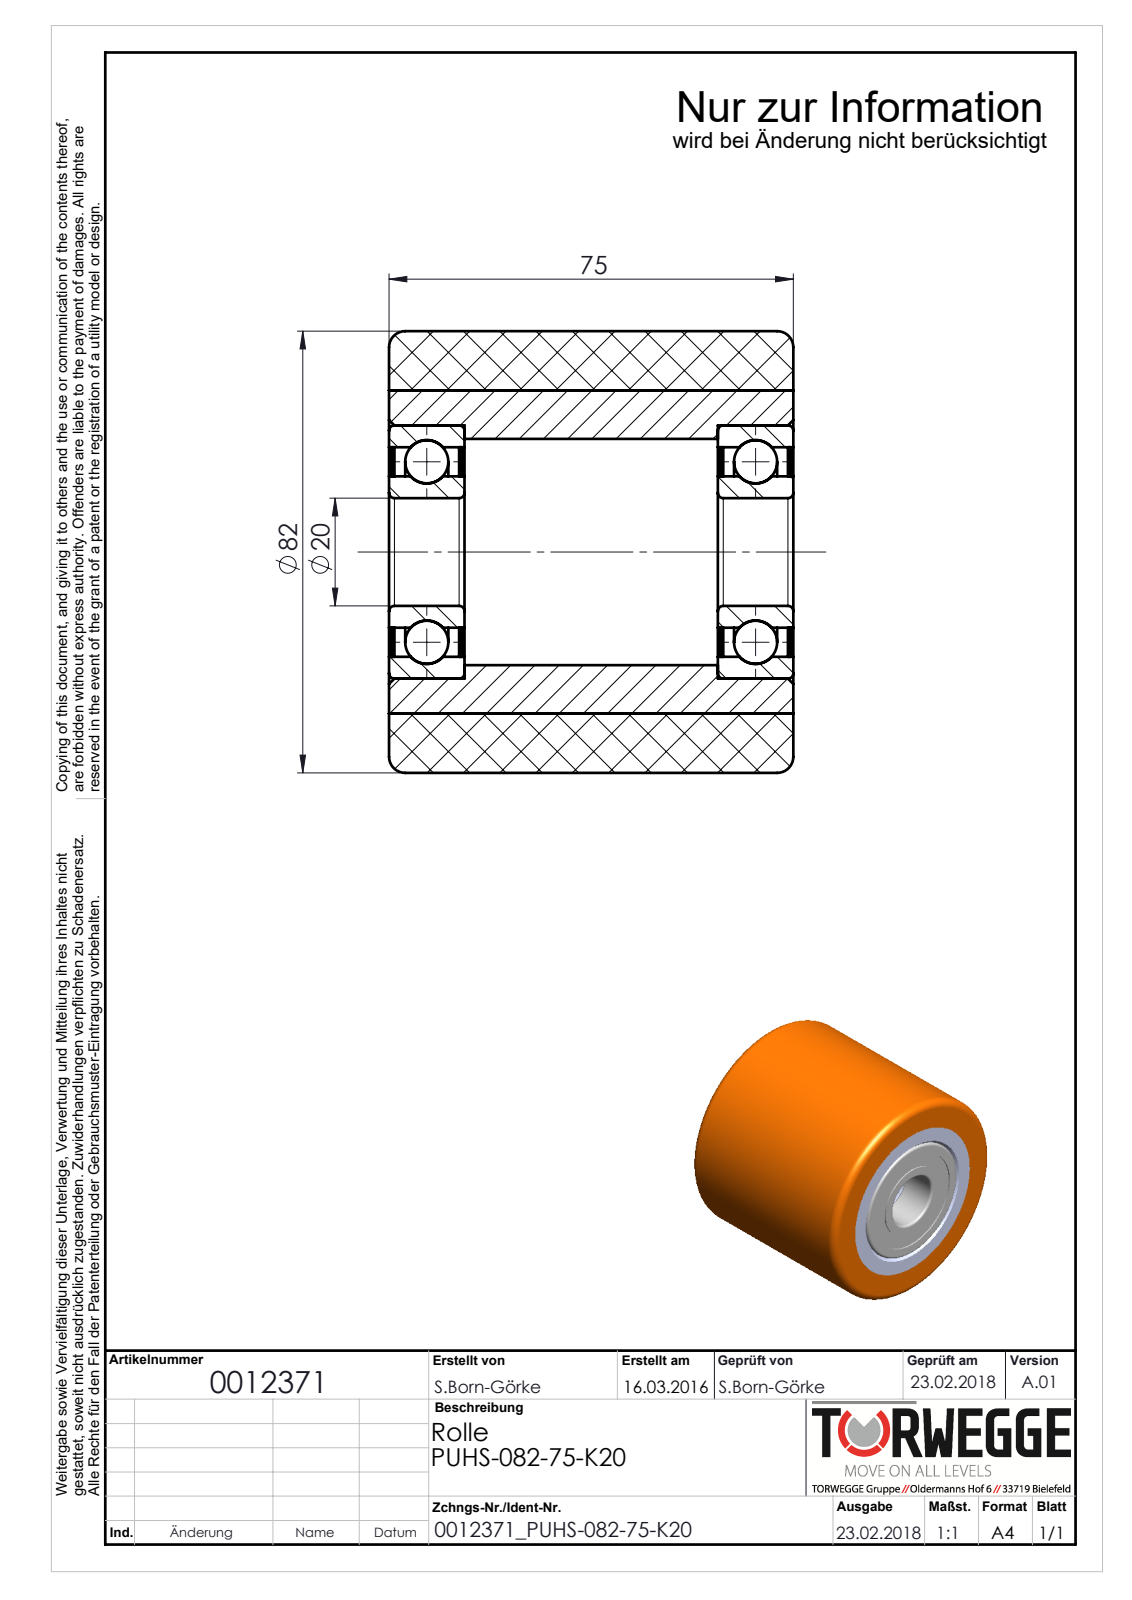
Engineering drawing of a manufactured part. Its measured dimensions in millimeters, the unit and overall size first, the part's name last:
Units: millimetres
Overall size (bounding box): 82 × 82 × 75
Round holes (diameter × count): ⌀20 ×1, ⌀28.1 ×1, ⌀38.9 ×1, ⌀42 ×1, ⌀47 ×1, ⌀60 ×1
Round bosses / shafts (diameter × count): ⌀82 ×1
Main face-to-face distances: 0.5, 61, 13, 75, 1, 13.5, 61.5, 12.5, 60.5, 14
Volume: 314 137 mm³ · Surface area: 90 317 mm²
Bodies: 12 solids, 118 faces (22 planar, 52 cylindrical, 44 other)
Part name (STEP PRODUCT): 0012371_PUHS-082-75-K20
STEP written by: SolidWorks 2016 (AUTOMOTIVE_DESIGN)
